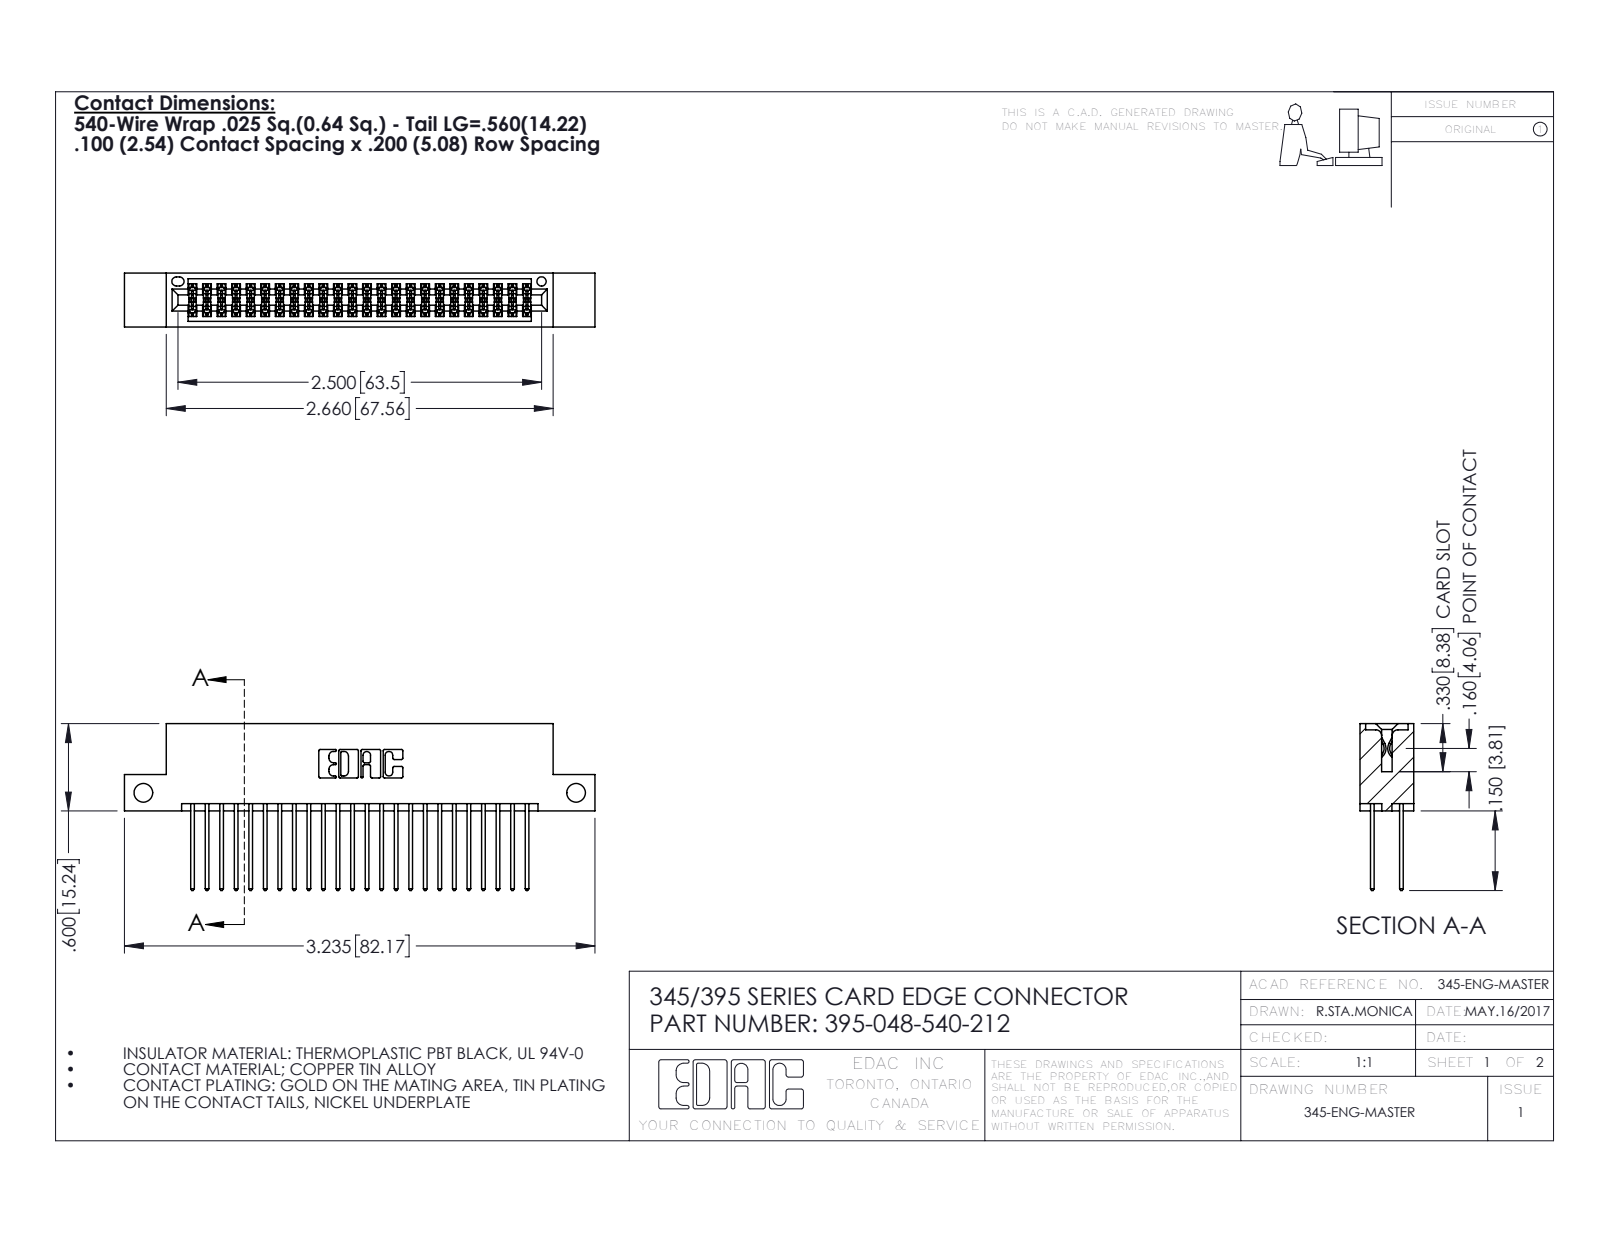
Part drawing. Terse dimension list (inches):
name: 345-292-001_345-293-140; 395-048-540-212; 345 Part_Flush Mounting Lugs - Side Mount
written by: SolidWorks 2016 (CONFIG_CONTROL_DESIGN)
unit: in
bodies: 49 solids, 2526 faces (1664 planar, 862 cylindrical, 0 other)
size: 3.235 × 1.147 × 0.37
volume: 0.483 in³; area: 18.68 in²
holes: 2× ⌀0.128, 1× ⌀0.064
rounds: 72× R0.006, 48× R0.01, 22× R0.01, 6× R0.007, 6× R0.031, 3× R0.026, 2× R0.014, 2× R0.019
face distances: 0.298, 0.072, 0.2, 0.098, 0.272, 0.025, 0.37, 0.225, 0.175, 0.149
hole spacings: 2.975
